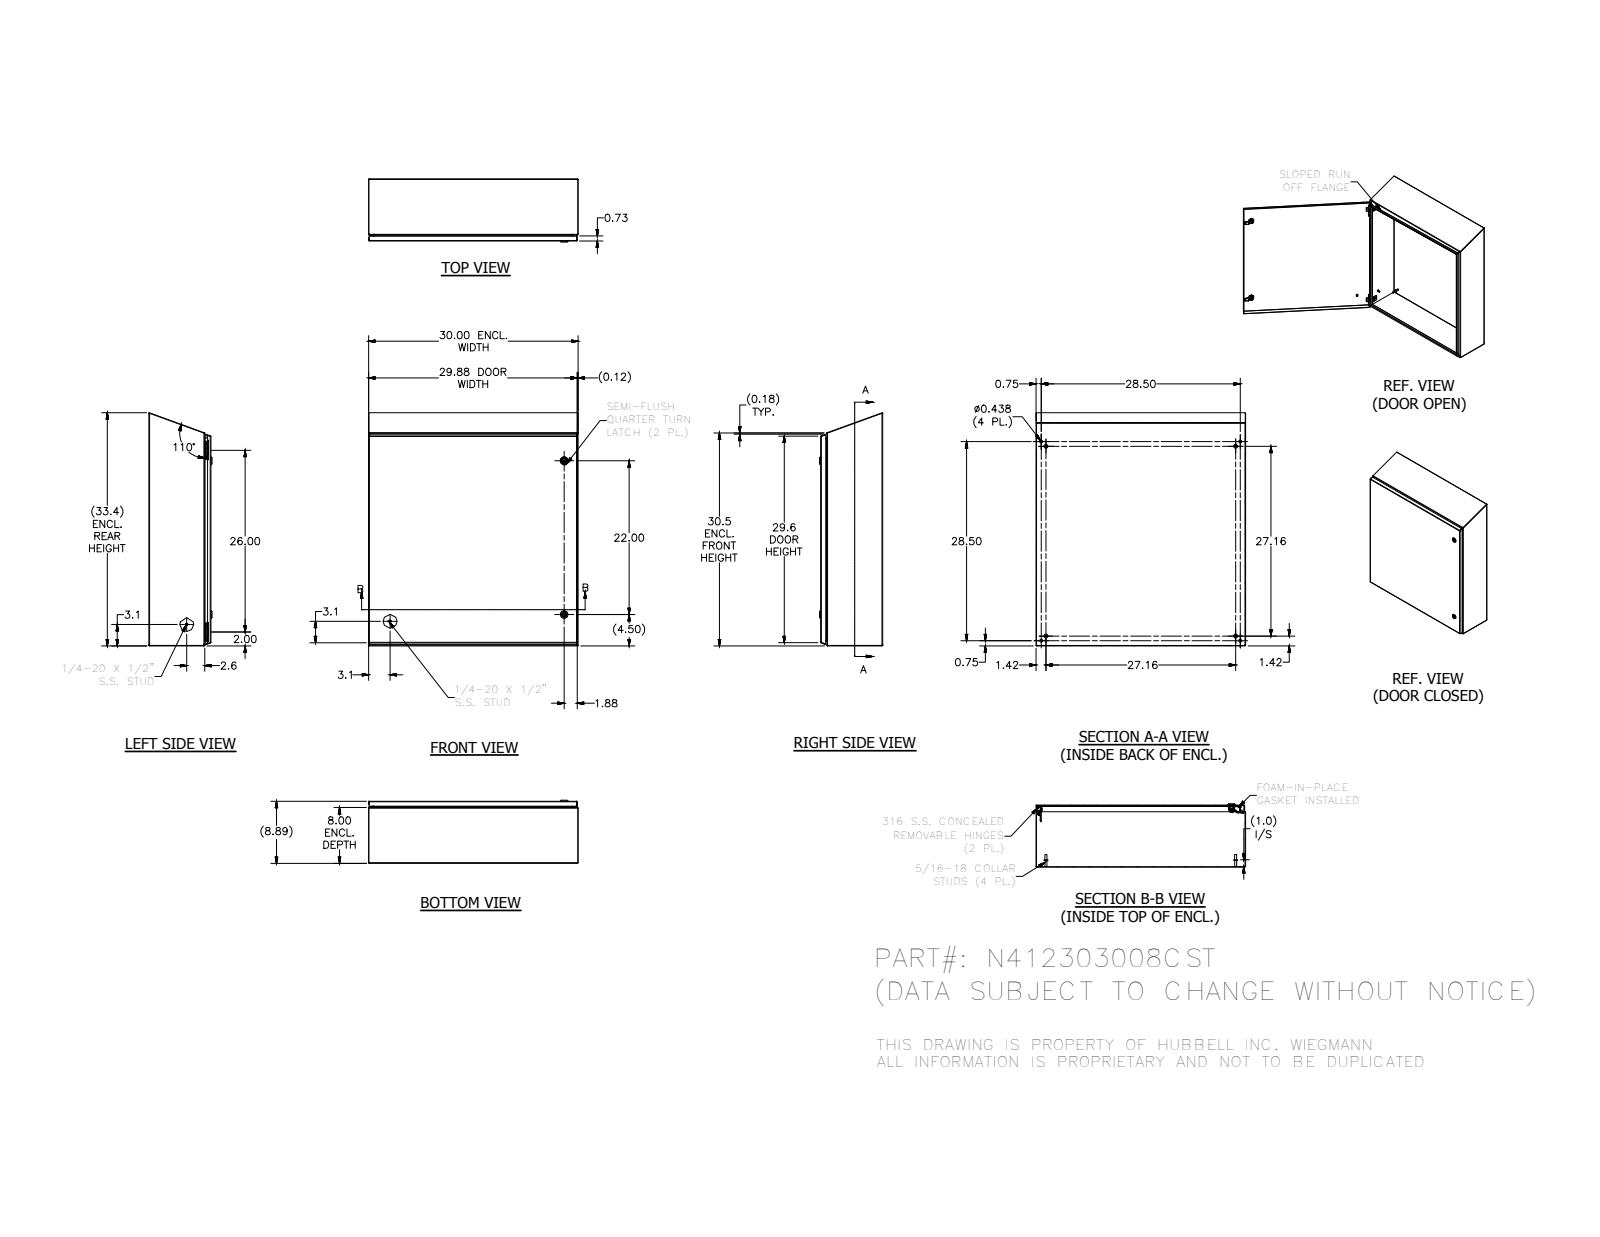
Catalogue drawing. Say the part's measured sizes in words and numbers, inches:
The part is named "N412_CST-assm; N412303008CSTB3S; HFW3161; HFW328176 (+8 more)". Its 3-D file was written by "Autodesk Inventor 2012 (AUTOMOTIVE_DESIGN)". It is 40 solids with 1934 faces: 775 planar, 694 cylindrical and 465 other. Overall it measures 52.003 by 30 by 9.044 inches. Its volume is 233.3 cubic inches and its surface area 6 362 square inches. Round holes: 4 of diameter 0.093, 4 of diameter 0.152, 4 of diameter 0.167, 4 of diameter 0.172, 4 of diameter 0.187, 4 of diameter 0.437, 3 of diameter 0.156, 2 of diameter 0.197, 2 of diameter 0.315, 2 of diameter 0.394, 2 of diameter 0.402, 2 of diameter 0.634. Round bosses or shafts: 10 of diameter 0.25, 4 of diameter 0.563, 4 of diameter 0.36, 4 of diameter 0.32, 4 of diameter 0.3, 4 of diameter 0.275, 4 of diameter 0.256, 4 of diameter 0.164. Partial cylindrical surfaces (rounded edges, fillets, slot ends): 54 of radius 0.012, 29 of radius 0.031, 26 of radius 0.05, 23 of radius 0.02, 19 of radius 0.105, 18 of radius 0.016, 16 of radius 0.125, 8 of radius 0.032. The main face-to-face distances are 0.074, 8.813, 8.887, 8.739, 29.926, 30, 29.852, 7.926, 0.887, 0.813. The hole center spacings are 26, 28.5, 0.5, 0.656, 0.66, 0.984, 1.307, 1.311.
